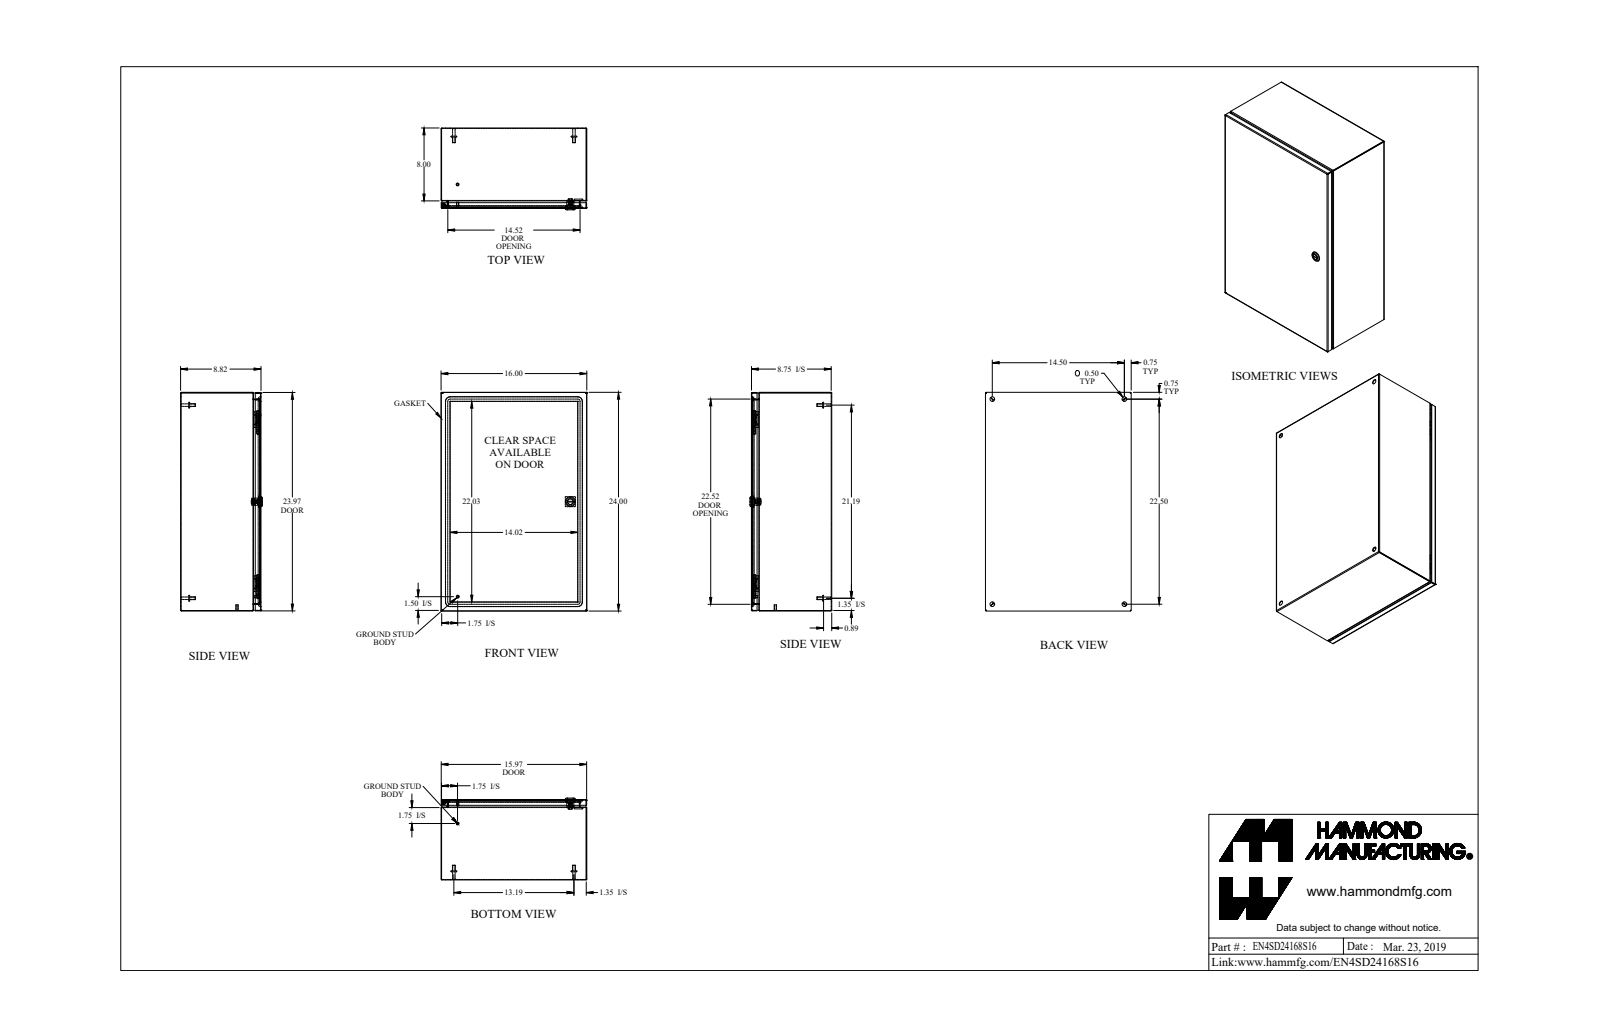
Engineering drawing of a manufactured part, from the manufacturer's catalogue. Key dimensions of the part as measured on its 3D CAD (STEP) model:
Part name (STEP PRODUCT): EN4SD24168S16_Default
STEP written by: SolidWorks 2019 (CONFIG_CONTROL_DESIGN)
Units: inches
Bodies: 22 solids, 657 faces (303 planar, 212 cylindrical, 142 other)
Overall size (bounding box): 24 × 16 × 8.981
Volume: 97.01 in³ · Surface area: 3 308 in²
Round holes (diameter × count): ⌀0.5 ×5, ⌀0.172 ×1, ⌀0.197 ×1, ⌀0.24 ×1, ⌀0.242 ×1, ⌀0.387 ×1, ⌀0.63 ×1, ⌀0.768 ×1
Round bosses / shafts (diameter × count): ⌀0.313 ×6, ⌀0.625 ×4, ⌀0.275 ×4, ⌀0.25 ×2, ⌀1.1 ×1, ⌀0.785 ×1, ⌀0.625 ×1, ⌀0.525 ×1
Partial cylindrical surfaces — rounded edges, fillets, slot ends (radius × count): R0.029 ×21, R0.086 ×21, R0.188 ×12, R0.006 ×4, R0.062 ×4, R0.25 ×4, R0.499 ×4, R0.125 ×2
Main face-to-face distances: 0.057, 0.057, 8.707, 8.764, 8.764, 8.821, 15.943, 23.943, 15.886, 16
Hole centre spacings: 11.3, 14.5, 17.528, 22.5, 26.767
